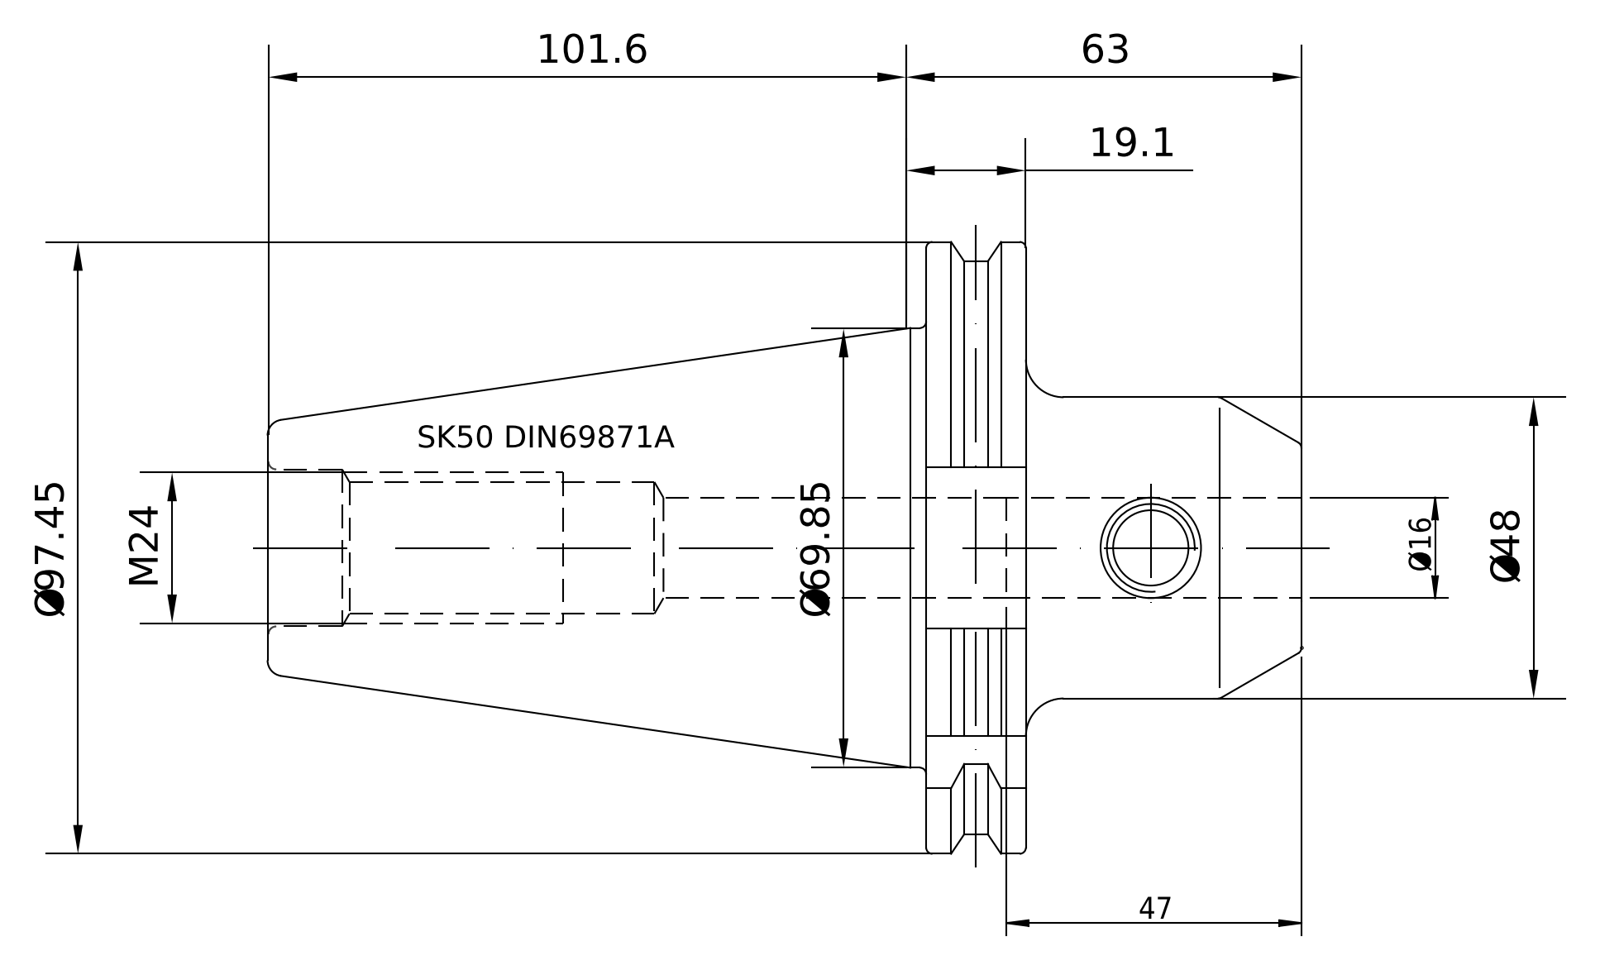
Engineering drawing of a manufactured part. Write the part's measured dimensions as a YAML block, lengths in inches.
part_name: "50-300-16"
step_written_by: "PRO/ENGINEER BY PARAMETRIC TECHNOLOGY CORPORATION, 2010430 (CONFIG_CONTROL_DESIGN)"
units: inches
bodies: {solids: 1, faces: 103, planar: 21, cylindrical: 32, other: 50}
overall_size: [6.48, 3.837, 3.701]
volume: 24.41
surface_area: 80.48
round_holes:
  - {diameter: 0.472, count: 1}
  - {diameter: 0.551, count: 1}
  - {diameter: 0.63, count: 1}
  - {diameter: 0.817, count: 1}
  - {diameter: 0.985, count: 1}
  - {diameter: 1.012, count: 1}
round_bosses_or_shafts:
  - {diameter: 3.583, count: 1}
  - {diameter: 2.722, count: 1}
  - {diameter: 1.89, count: 1}
  - {diameter: 0.945, count: 1}
partial_cylinders:
  - {radius: 0.069, count: 5}
  - {radius: 1.919, count: 1}
face_to_face_distances: [0.624, 2.354, 1.73, 4.126, 4.75, 6.48, 2.866, 1.016, 4.193, 0.067]
